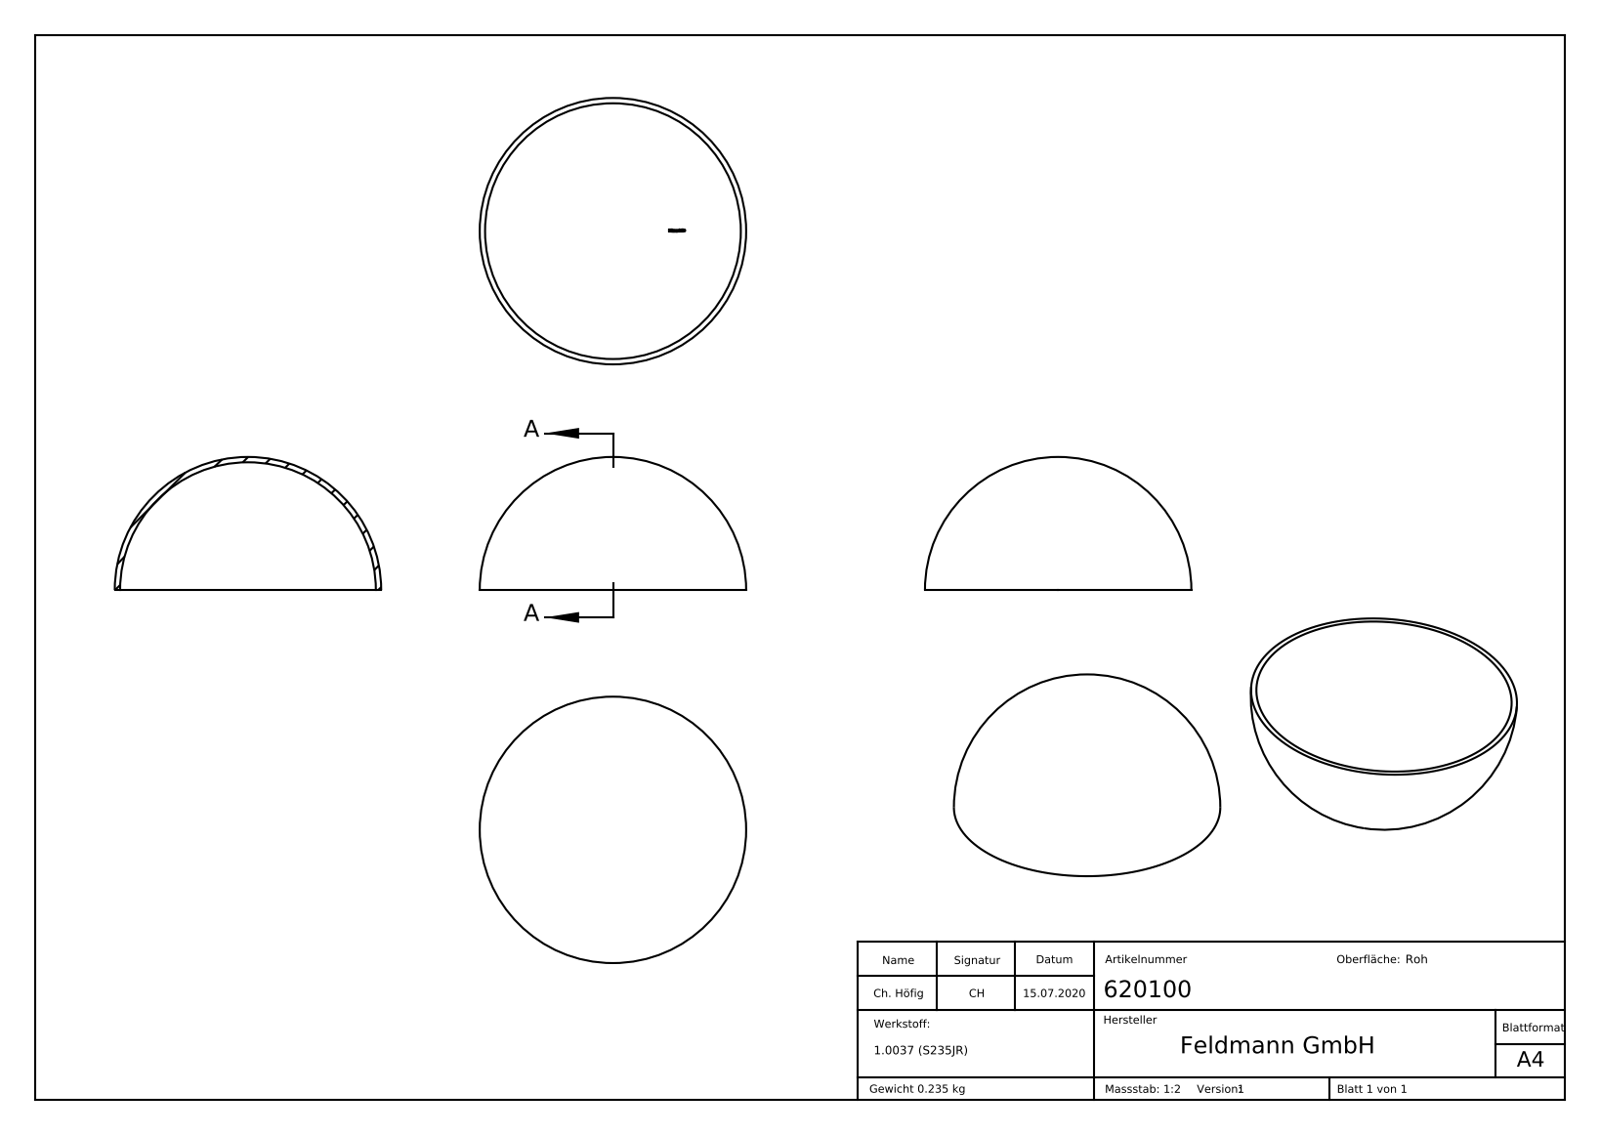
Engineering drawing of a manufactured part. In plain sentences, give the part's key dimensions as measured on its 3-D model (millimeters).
The part is named "620100". Its 3-D file was written by "SolidWorks 2018 (CONFIG_CONTROL_DESIGN)". It is 1 solid with 183 faces: 70 planar, 0 cylindrical and 113 other. Overall it measures 100 by 100 by 50 millimeters. Its volume is 30 176 cubic millimeters and its surface area 30 804 square millimeters. The main face-to-face distances are 1.19, 0.55, 0.5, 0.81, 0.66, 3.1, 1.74, 0.53, 0.45, 1.31.
